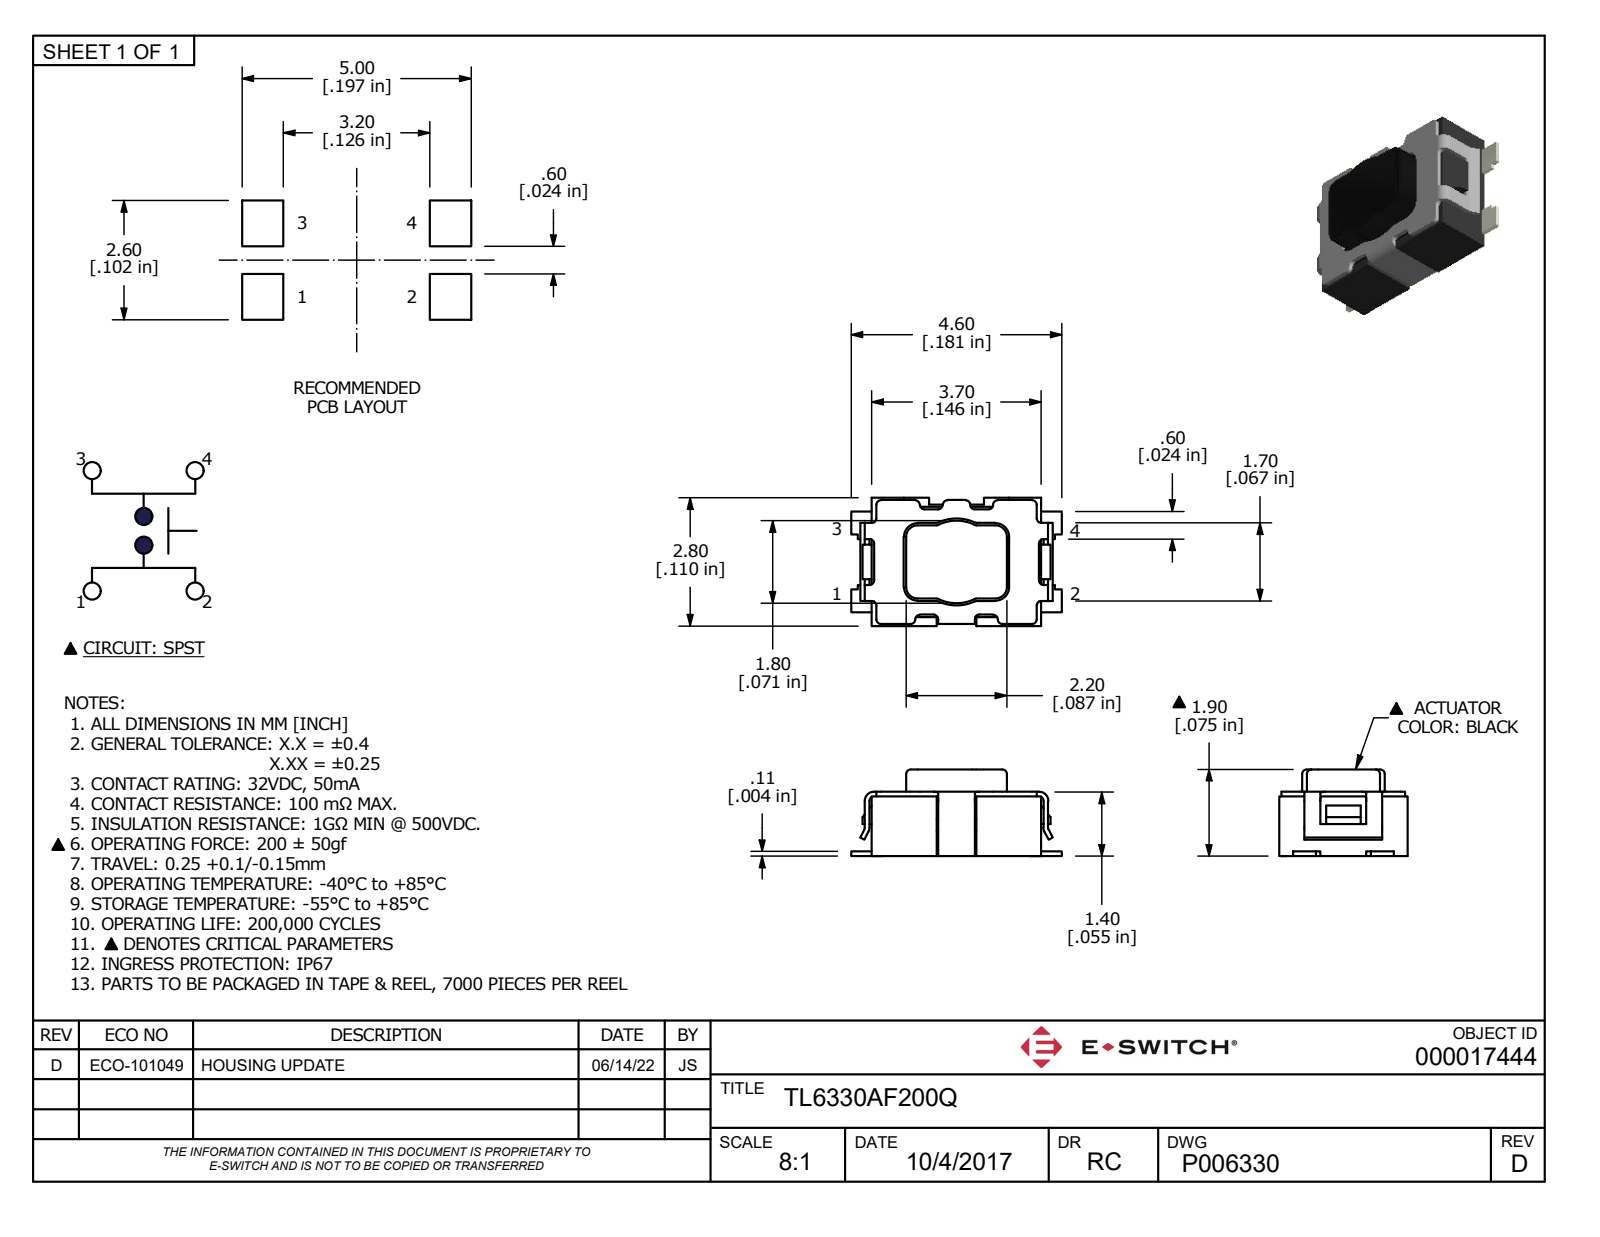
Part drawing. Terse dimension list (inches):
written by: Autodesk Inventor 2012 (CONFIG_CONTROL_DESIGN)
unit: in
bodies: 1 solid, 245 faces (164 planar, 71 cylindrical, 10 other)
size: 0.181 × 0.11 × 0.075
volume: 0.001 in³; area: 0.111 in²
holes: 2× ⌀0.02, 1× ⌀0.035
rounds: 43× R0.004, 5× R0.008, 4× R0.01, 4× R0.012, 1× R0.035, 1× R0.037
face distances: 0.022, 0.031, 0.024, 0.033, 0.055, 0.028, 0.102, 0.051, 0.03, 0.146
hole spacings: 0.047, 0.094
